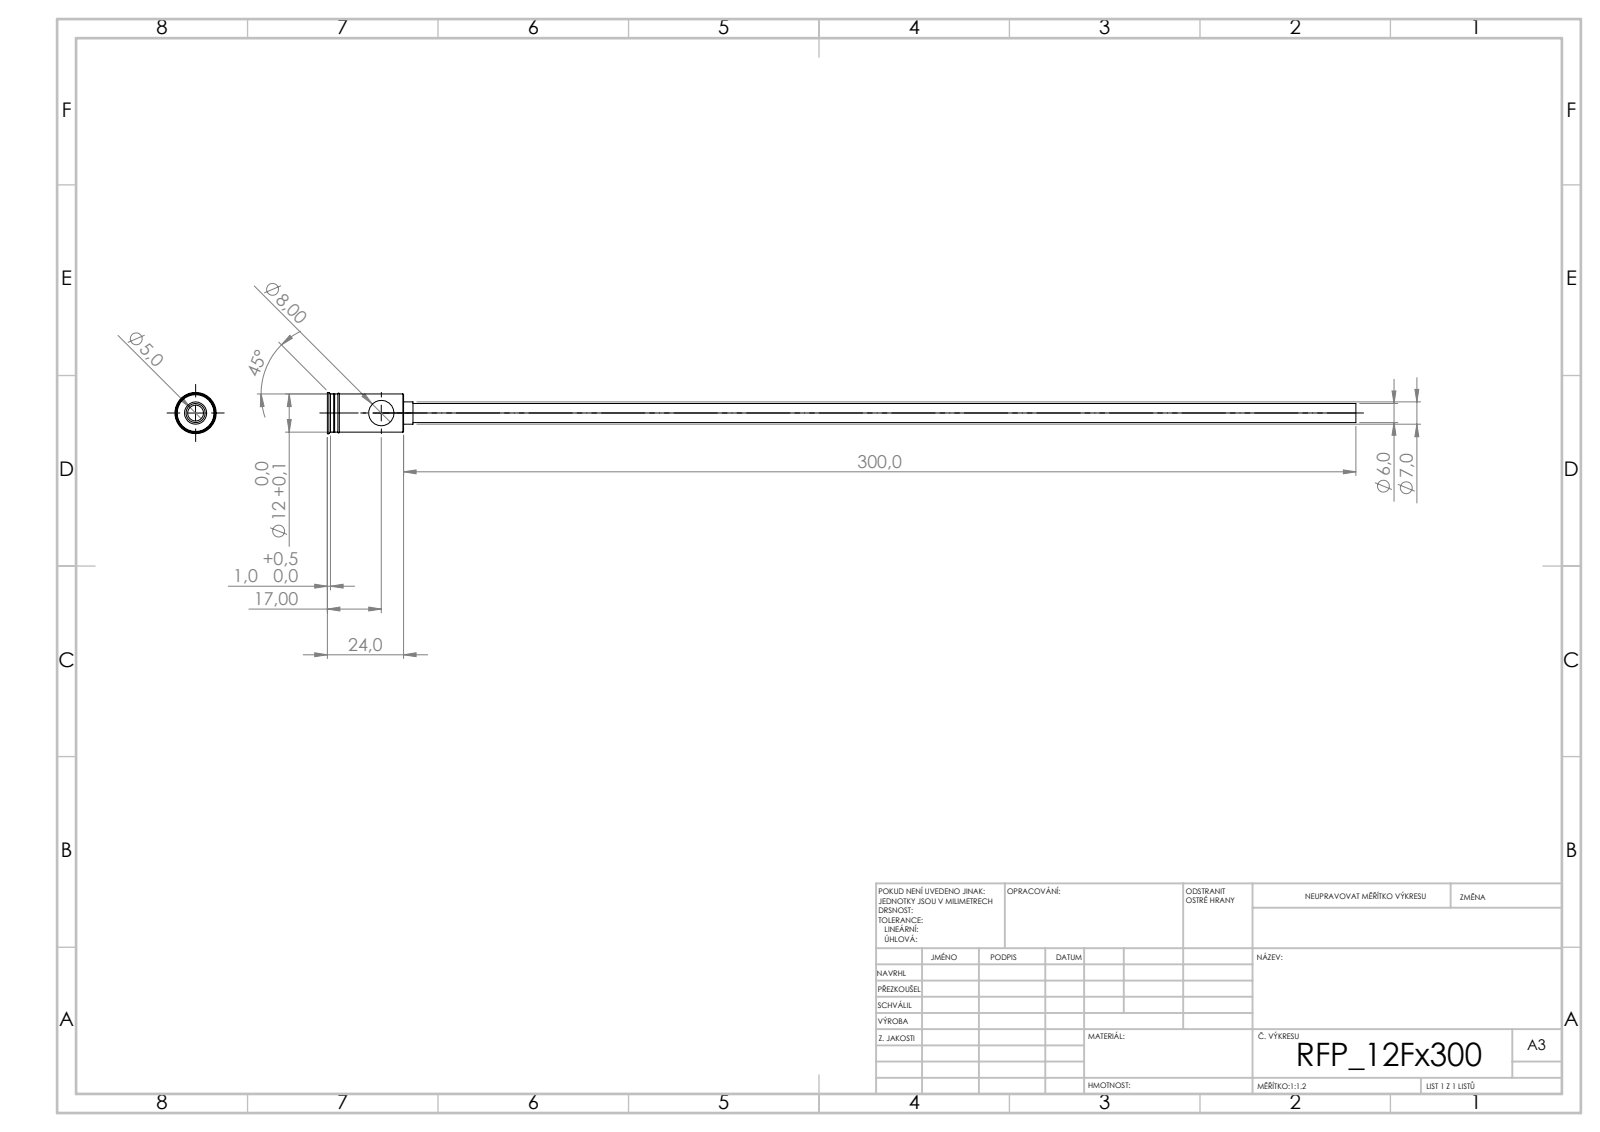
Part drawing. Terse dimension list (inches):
written by: SolidWorks 2019 (CONFIG_CONTROL_DESIGN)
unit: in
bodies: 1 solid, 44 faces (20 planar, 16 cylindrical, 8 other)
size: 12.756 × 0.512 × 0.512
volume: 0.282 in³; area: 18.26 in²
holes: 1× ⌀0.197, 1× ⌀0.315
bosses: 1× ⌀0.512, 1× ⌀0.472, 1× ⌀0.276, 1× ⌀0.236
face distances: 0.945, 0.866, 0.079, 0.291, 0.854, 0.091, 0.118, 0.972, 0.984, 1.063
